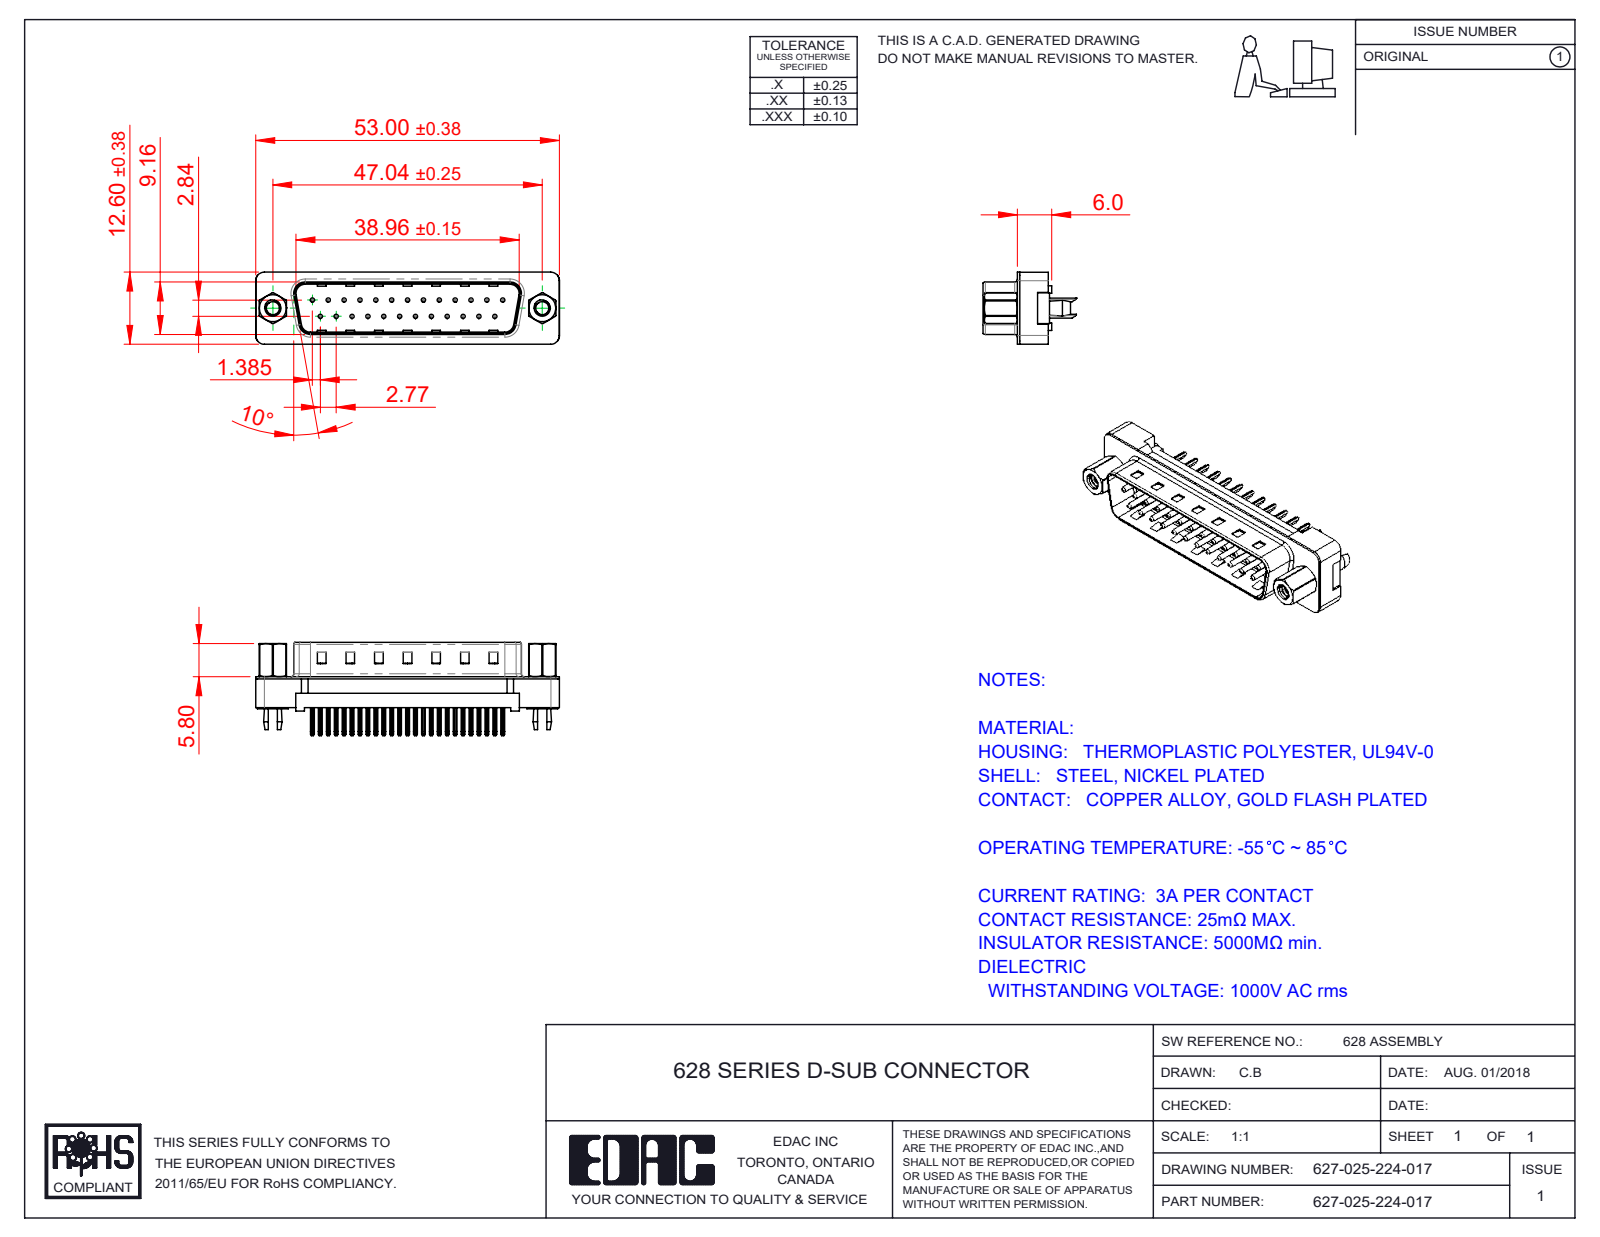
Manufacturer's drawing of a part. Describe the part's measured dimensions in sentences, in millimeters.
The part is named "627 Plastic Body Housing_25 Contacts; 627 PB Contact Row 1_24; 627 PB 4-40 Threaded Rivet with Boardlock; 627 PB Shell_25 Contacts (+3 more)". Its 3-D file was written by "SolidWorks 2020 (CONFIG_CONTROL_DESIGN)". It is 31 solids with 1909 faces: 1185 planar, 570 cylindrical and 154 other. Overall it measures 53.04 by 16.3 by 12.6 millimeters. Its volume is 2 797 cubic millimeters and its surface area 6 471 square millimeters. Round holes: 25 of diameter 0.35, 25 of diameter 0.85, 2 of diameter 2.26, 2 of diameter 2.29, 2 of diameter 4, 2 of diameter 4.8, 2 of diameter 5. Round bosses or shafts: 25 of diameter 0.75, 2 of diameter 4.9, 2 of diameter 2.79. Partial cylindrical surfaces (rounded edges, fillets, slot ends): 50 of radius 0.25, 25 of radius 0.12, 8 of radius 0.5, 8 of radius 1.5, 4 of radius 0.9, 4 of radius 1.6, 4 of radius 2, 2 of radius 0.4. The main face-to-face distances are 0.4, 2.5, 8.76, 2.9, 5.4, 1.58, 5, 1.3, 6.5, 0.68. The hole center spacings are 3.16, 5.54, 2.77, 11.08, 8.31, 5.03, 13.85, 16.62.
